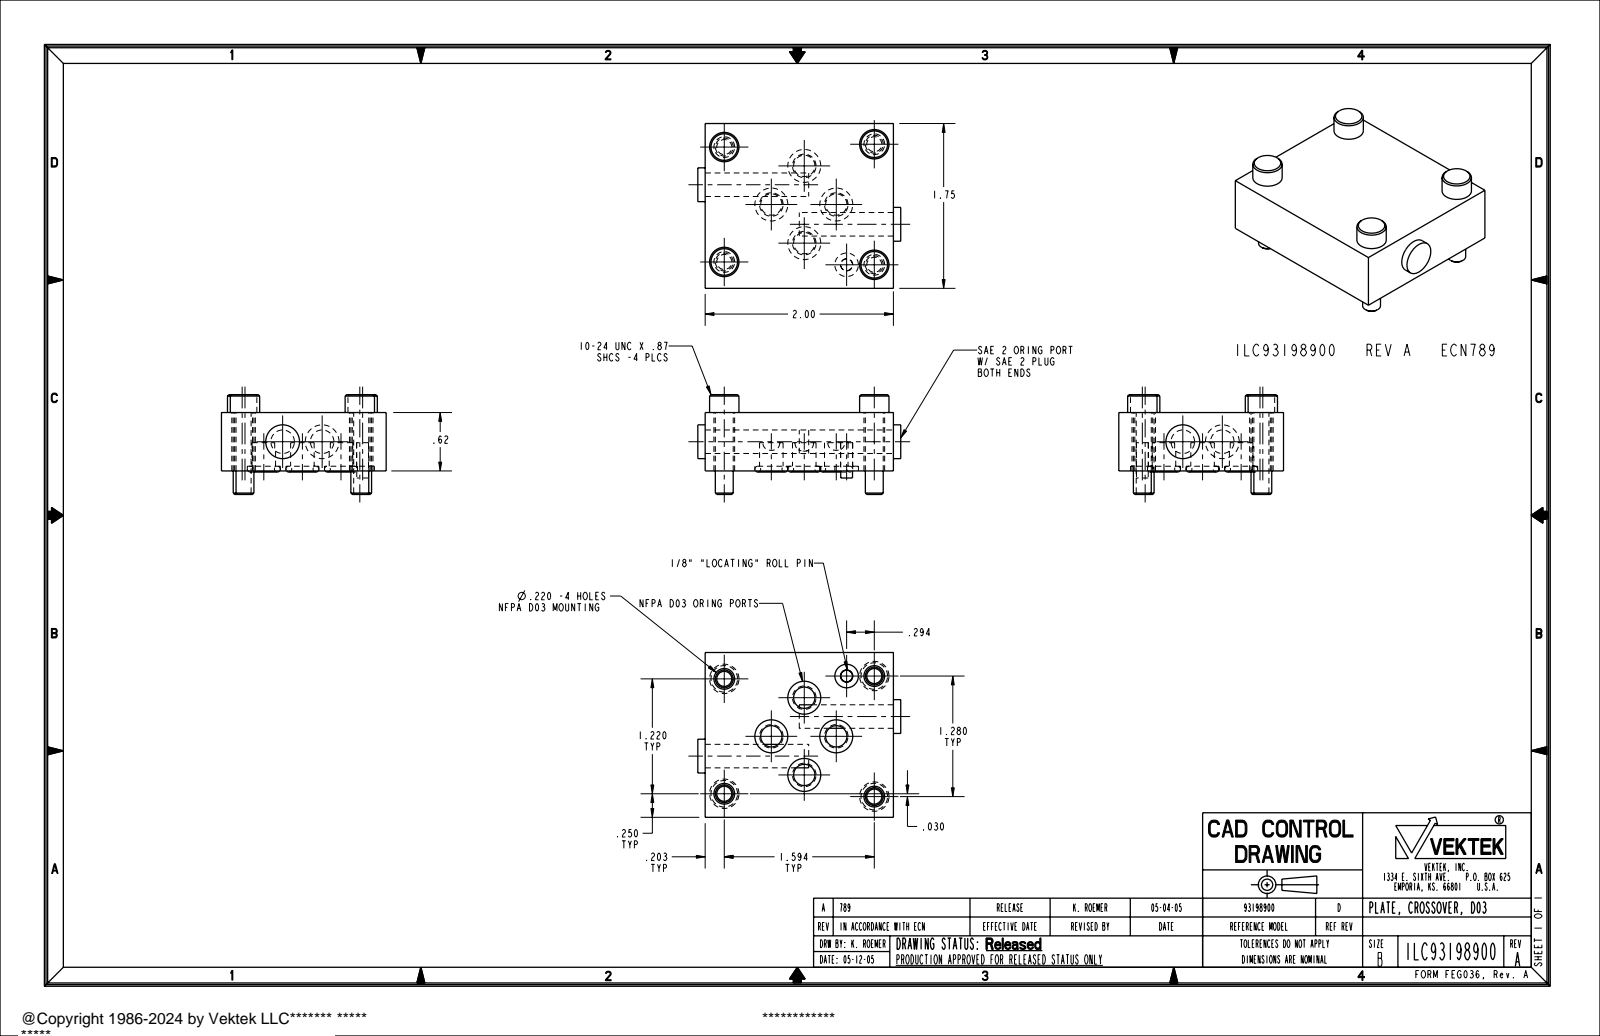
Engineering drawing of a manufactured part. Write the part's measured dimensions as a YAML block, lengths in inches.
part_name: "ILC93198900"
step_written_by: "PRO/ENGINEER BY PARAMETRIC TECHNOLOGY CORPORATION, 2004290 (AUTOMOTIVE_DESIGN_CC2)"
units: inches
bodies: {solids: 5, faces: 121, planar: 35, cylindrical: 54, other: 32}
overall_size: [2.156, 1.75, 1.06]
volume: 2.087
surface_area: 20.02
round_holes:
  - {diameter: 0.25, count: 7}
  - {diameter: 0.22, count: 4}
  - {diameter: 0.35, count: 4}
  - {diameter: 0.13, count: 1}
round_bosses_or_shafts:
  - {diameter: 0.312, count: 4}
  - {diameter: 0.19, count: 4}
  - {diameter: 0.359, count: 2}
  - {diameter: 0.125, count: 1}
face_to_face_distances: [0.62, 1.75, 2, 0.25, 0.3, 0.81, 0.19, 0.05, 0.57, 0.76]
hole_center_spacings: [0.778, 0.873, 1.287, 1.328, 1.337, 1.594, 2.026, 0.294]
